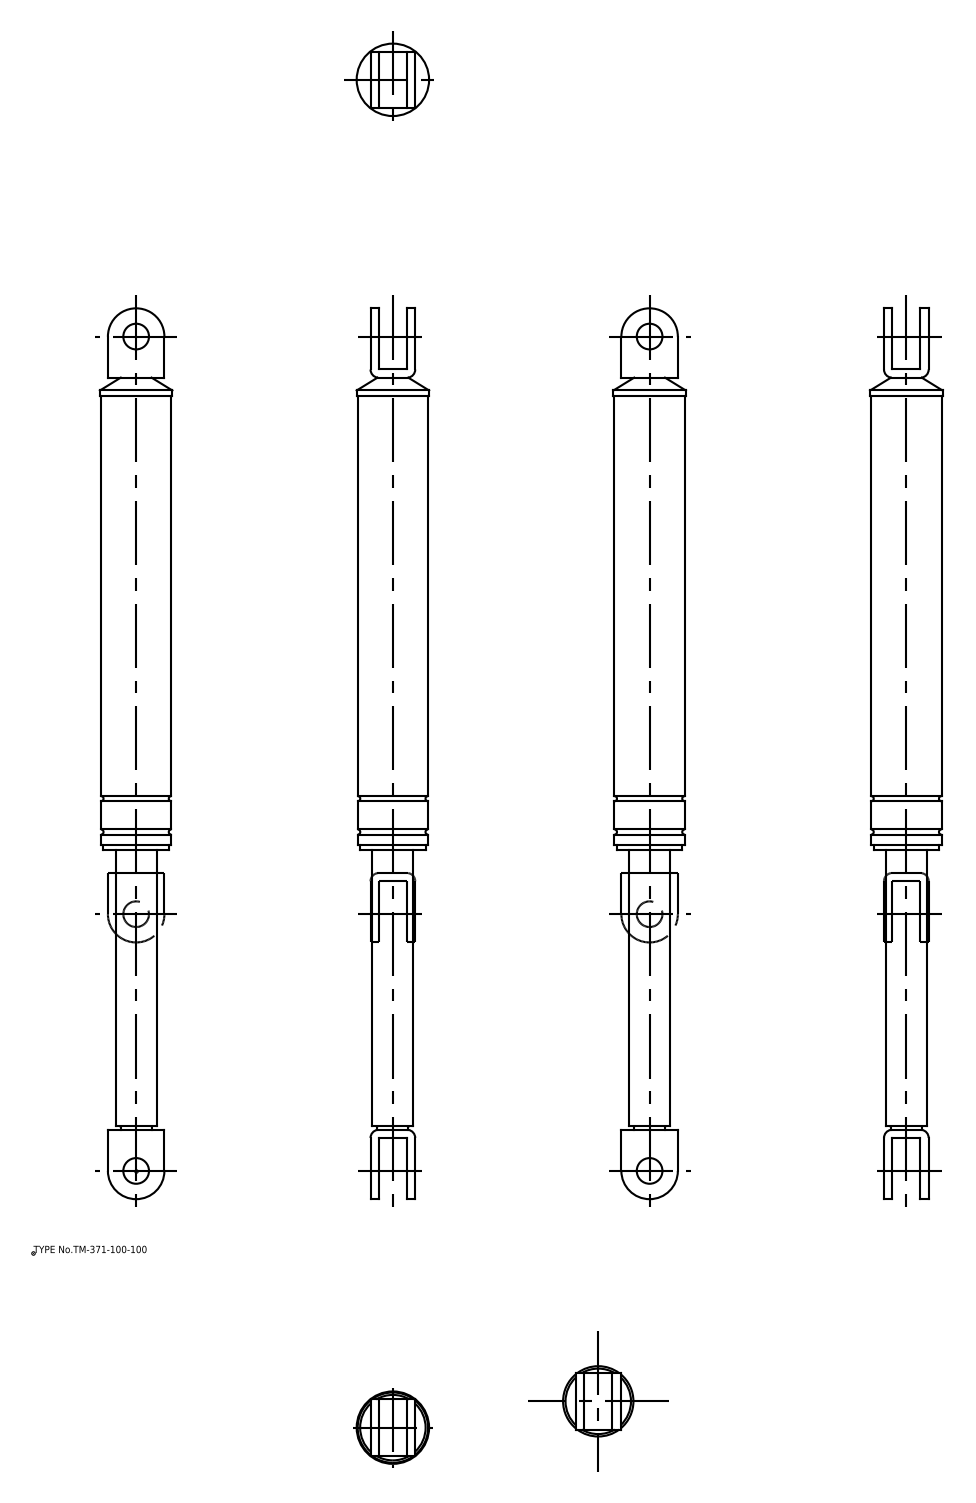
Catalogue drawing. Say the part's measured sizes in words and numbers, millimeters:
The part is named "TM_371_100_100; TM_371_100_100_div". Its 3-D file was written by "spGate 16.7.1 (AUTOMOTIVE_DESIGN)". It is 2 solids with 69 faces: 23 planar, 34 cylindrical and 12 other. Overall it measures 347 by 28.2 by 28.2 millimeters. Its volume is 135 969 cubic millimeters and its surface area 28 248 square millimeters. Round holes: 2 of diameter 10. Round bosses or shafts: 1 of diameter 28.2, 1 of diameter 27.4, 1 of diameter 25.5, 1 of diameter 16, 1 of diameter 12. Partial cylindrical surfaces (rounded edges, fillets, slot ends): 4 of radius 3.2, 2 of radius 11. The main face-to-face distances are 3.2, 14.2, 17.4, 11, 22, 296.2, 112.2, 299.4, 187.2, 184. The hole center spacings are 325.
